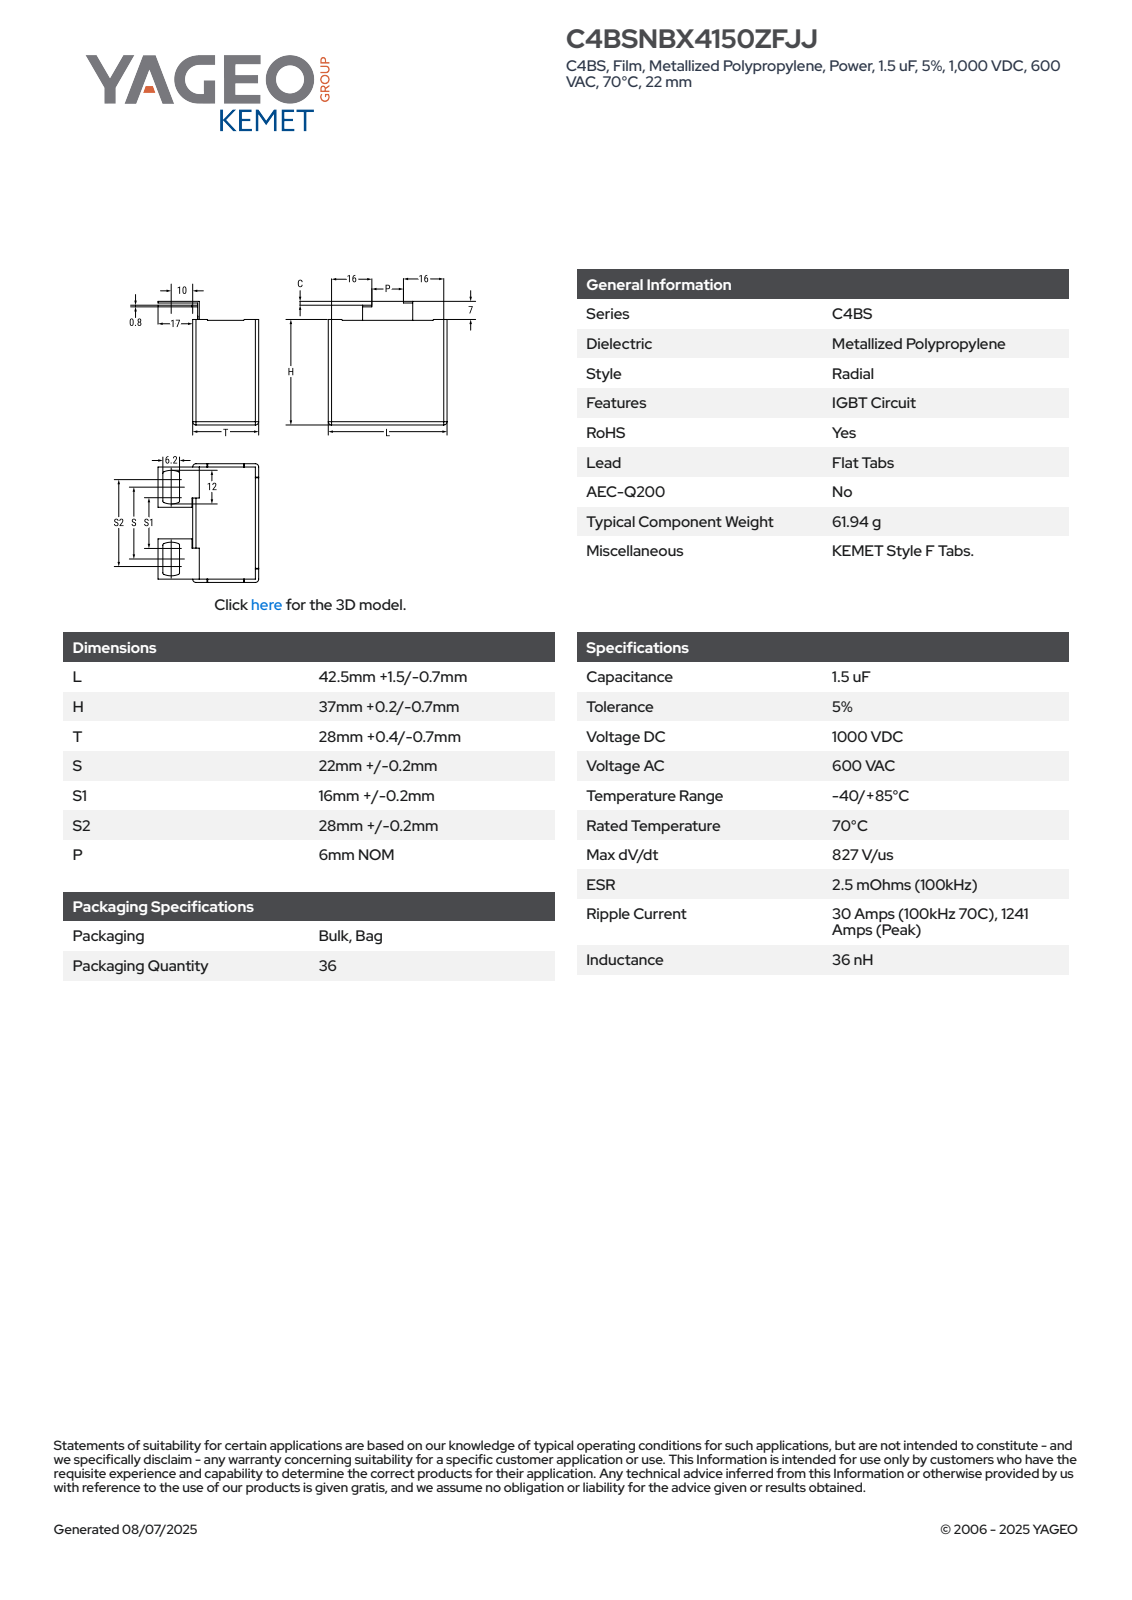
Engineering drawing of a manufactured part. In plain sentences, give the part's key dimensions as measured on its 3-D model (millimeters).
The part is named "CFP_C4BF_42.5X37X28_L44H37.2T28.4S22.2". Its 3-D file was written by "SolidWorks 2014 (AUTOMOTIVE_DESIGN)". It is 4 solids with 93 faces: 85 planar, 8 cylindrical and 0 other. Overall it measures 45.41 by 44.2 by 44 millimeters. Its volume is 47 041 cubic millimeters and its surface area 9 596 square millimeters. Partial cylindrical surfaces (rounded edges, fillets, slot ends): 4 of radius 4.6, 2 of radius 0.5. The main face-to-face distances are 28.4, 37.2, 44, 0.8, 6.2, 7, 44.2, 43.4, 2.8, 25.6.
